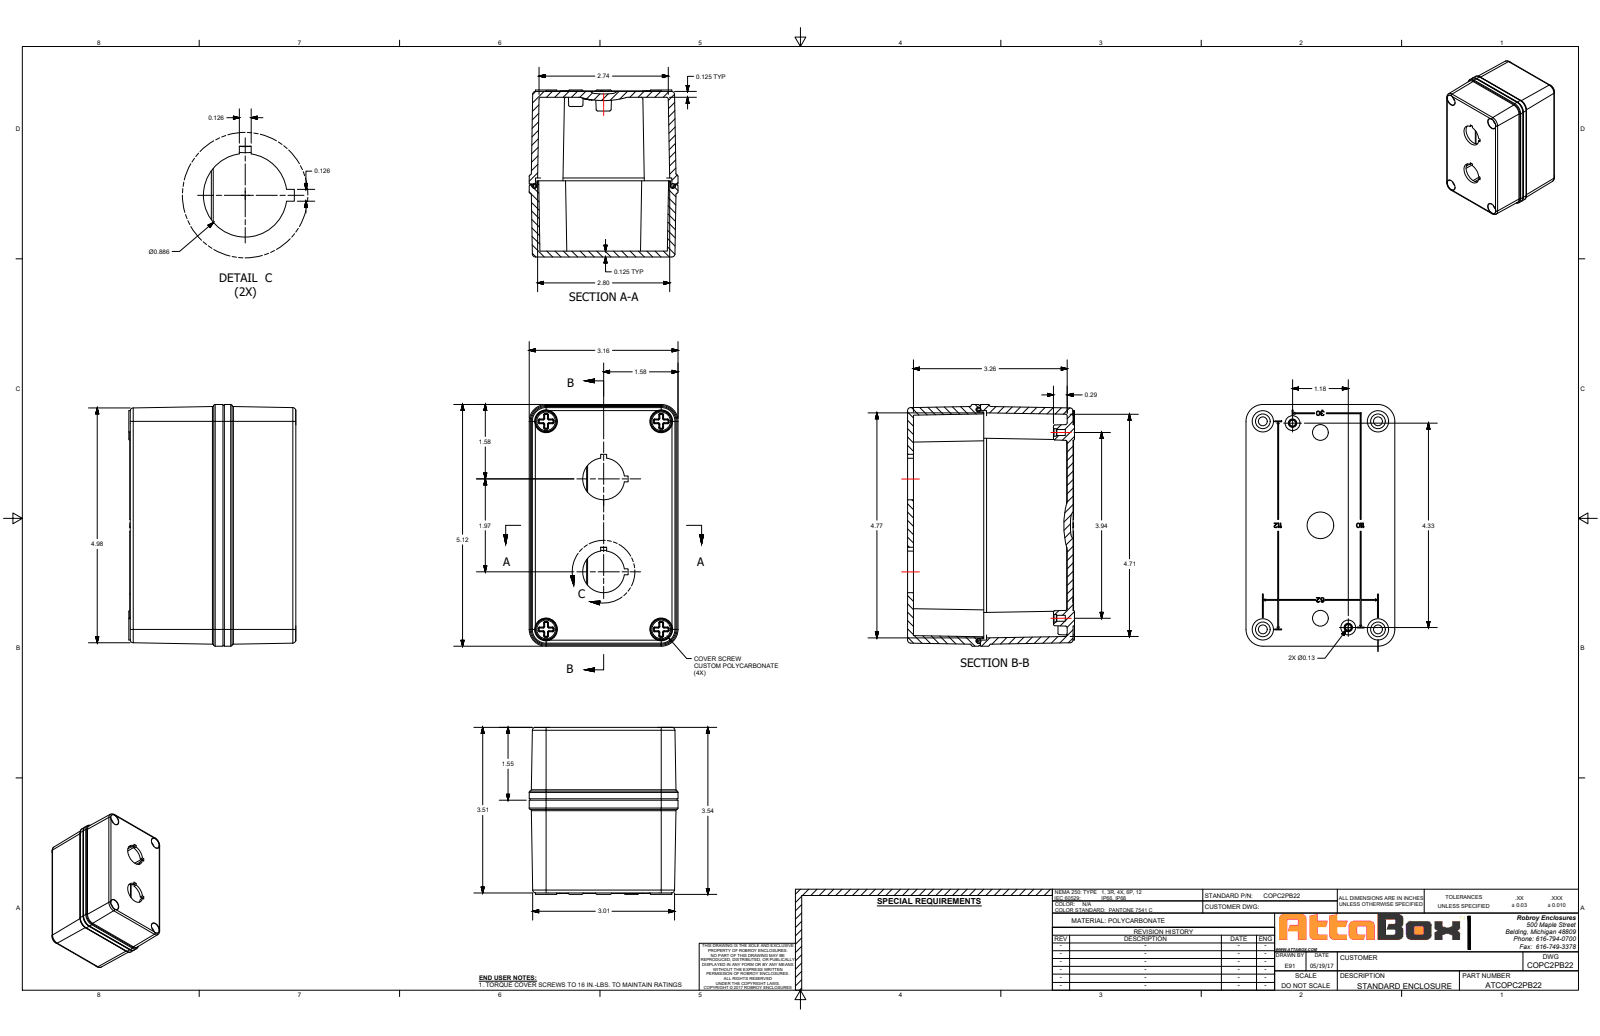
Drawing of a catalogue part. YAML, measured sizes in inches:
part_name: "COPC2PB22"
step_written_by: "SolidWorks 2018 (AUTOMOTIVE_DESIGN)"
units: inches
bodies: {solids: 7, faces: 1113, planar: 263, cylindrical: 469, other: 381}
overall_size: [5.124, 3.54, 3.155]
volume: 13.24
surface_area: 196.7
round_holes:
  - {diameter: 0.1, count: 6}
  - {diameter: 0.187, count: 4}
  - {diameter: 0.313, count: 4}
  - {diameter: 0.46, count: 4}
  - {diameter: 0.495, count: 3}
  - {diameter: 0.157, count: 2}
  - {diameter: 0.886, count: 2}
  - {diameter: 0.495, count: 1}
round_bosses_or_shafts:
  - {diameter: 0.45, count: 4}
  - {diameter: 0.433, count: 4}
  - {diameter: 0.276, count: 4}
  - {diameter: 0.335, count: 2}
  - {diameter: 0.333, count: 2}
  - {diameter: 0.315, count: 2}
  - {diameter: 0.312, count: 2}
  - {diameter: 0.1, count: 2}
partial_cylinders:
  - {radius: 0.02, count: 48}
  - {radius: 0.01, count: 32}
  - {radius: 0.015, count: 14}
  - {radius: 0.019, count: 12}
  - {radius: 0.03, count: 8}
  - {radius: 0.04, count: 8}
  - {radius: 0.08, count: 8}
  - {radius: 0.15, count: 8}
face_to_face_distances: [0.161, 3.51, 0.125, 3.385, 3.385, 3.26, 0.125, 2.801, 0.177, 1.965]
hole_center_spacings: [1.726, 3.415, 0.57, 0.631, 1.32, 1.811, 2.441, 3.204]
